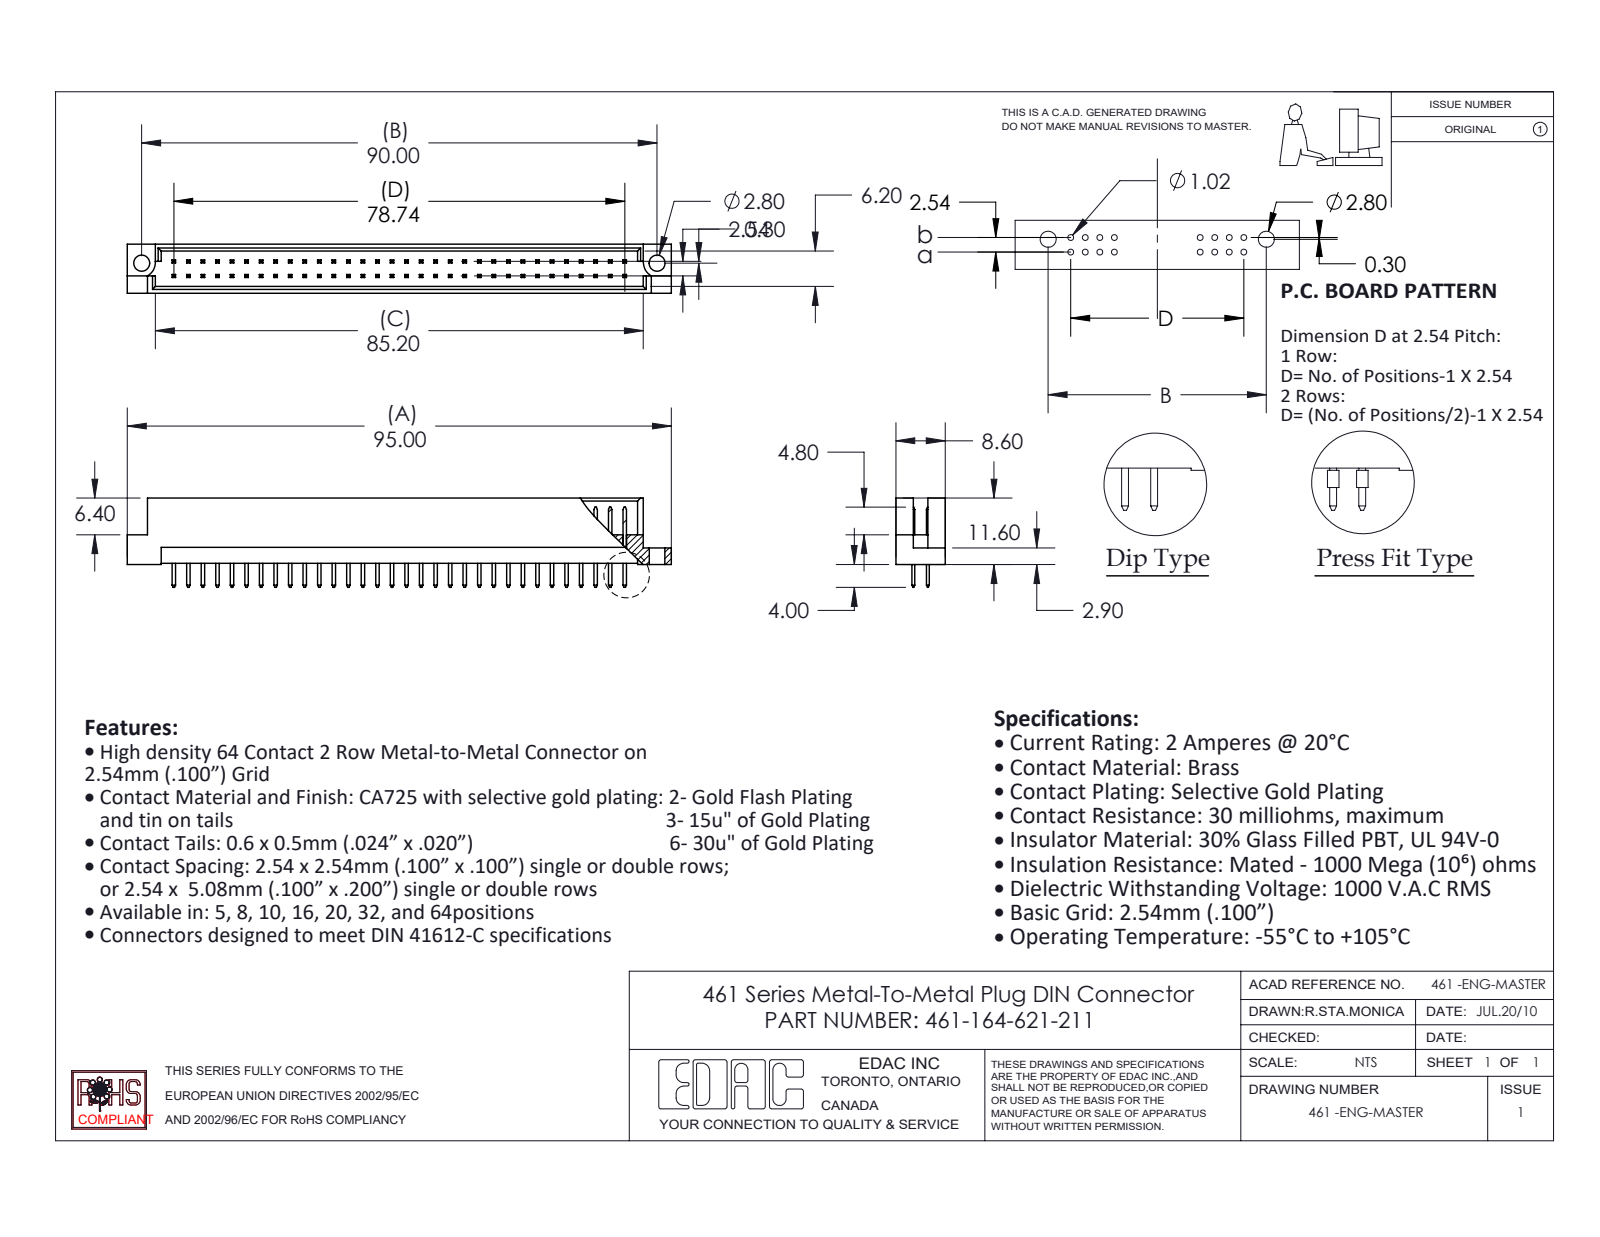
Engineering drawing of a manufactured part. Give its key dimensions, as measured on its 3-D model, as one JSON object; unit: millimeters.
{"part_name": "461 Part_64; 461-164-621-211; 461-290_21", "step_written_by": "SolidWorks 2020 (CONFIG_CONTROL_DESIGN)", "units": "millimeters", "bodies": {"solids": 65, "faces": 1201, "planar": 1194, "cylindrical": 7, "other": 0}, "overall_size": [95, 15.6, 8.6], "volume_mm3": 4918, "surface_area_mm2": 7618, "round_holes": [[2.8, 2]], "partial_cylinders_radius": [[2.8, 2]], "face_to_face_distances": [1.2, 7.4, 2.54, 8.6, 6.2, 3.28, 5.32, 2.08, 4.12, 2.78], "hole_center_spacings": [90]}
